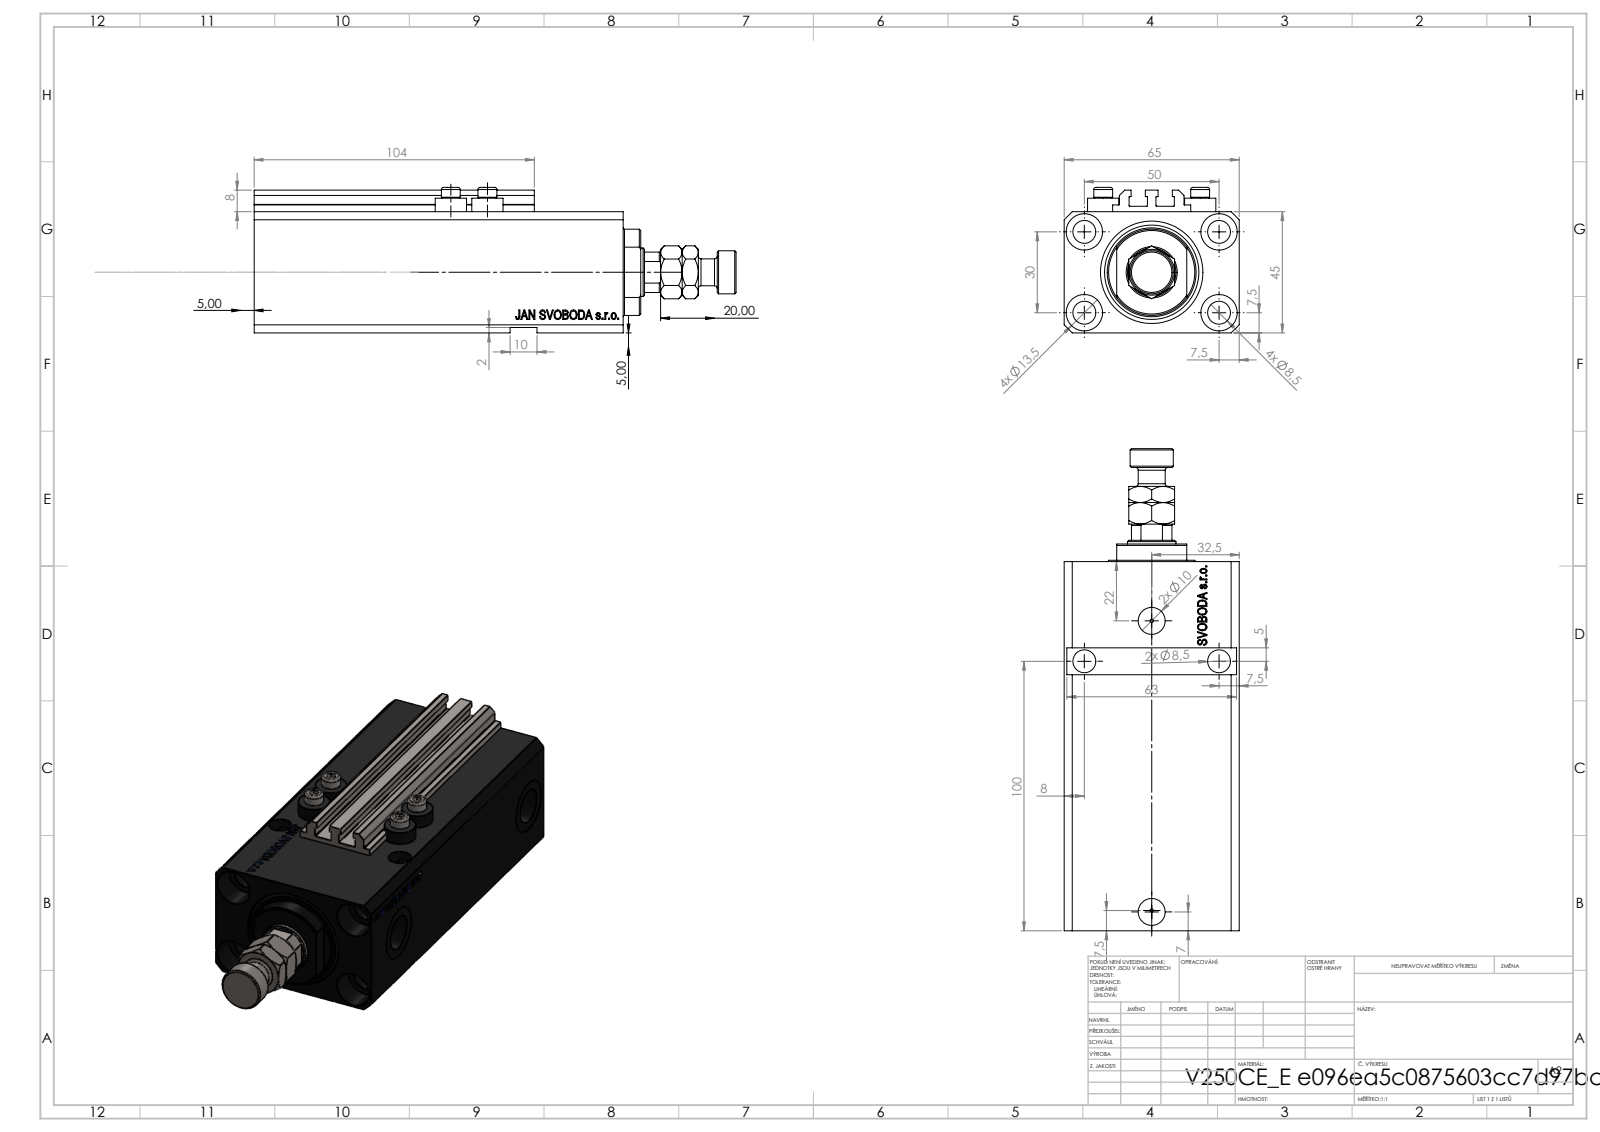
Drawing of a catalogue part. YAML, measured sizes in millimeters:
part_name: "ALLEN BOLT V250CE; MFA; V250CE_C_VCP; V250CE_E_Body (+1 more)"
step_written_by: "SolidWorks 2019 (CONFIG_CONTROL_DESIGN)"
units: millimeters
bodies: {solids: 9, faces: 1139, planar: 527, cylindrical: 150, other: 462}
overall_size: [179, 65, 54]
volume: 355919
surface_area: 95611
round_holes:
  - {diameter: 8.5, count: 9}
  - {diameter: 1.25, count: 4}
  - {diameter: 4, count: 4}
  - {diameter: 13.5, count: 4}
  - {diameter: 10, count: 2}
  - {diameter: 13.16, count: 2}
  - {diameter: 20, count: 2}
  - {diameter: 18, count: 1}
  - {diameter: 25, count: 1}
  - {diameter: 38, count: 1}
round_bosses_or_shafts:
  - {diameter: 11.6, count: 4}
  - {diameter: 7, count: 4}
  - {diameter: 16, count: 1}
  - {diameter: 10, count: 1}
partial_cylinders:
  - {radius: 0.2, count: 10}
  - {radius: 8.5, count: 1}
  - {radius: 16, count: 1}
face_to_face_distances: [45, 65, 47, 14, 2, 123, 2.5, 10, 20.5, 6]
hole_center_spacings: [29.15, 50, 13.6, 15.12, 27.89, 30, 33.61, 33.62]
